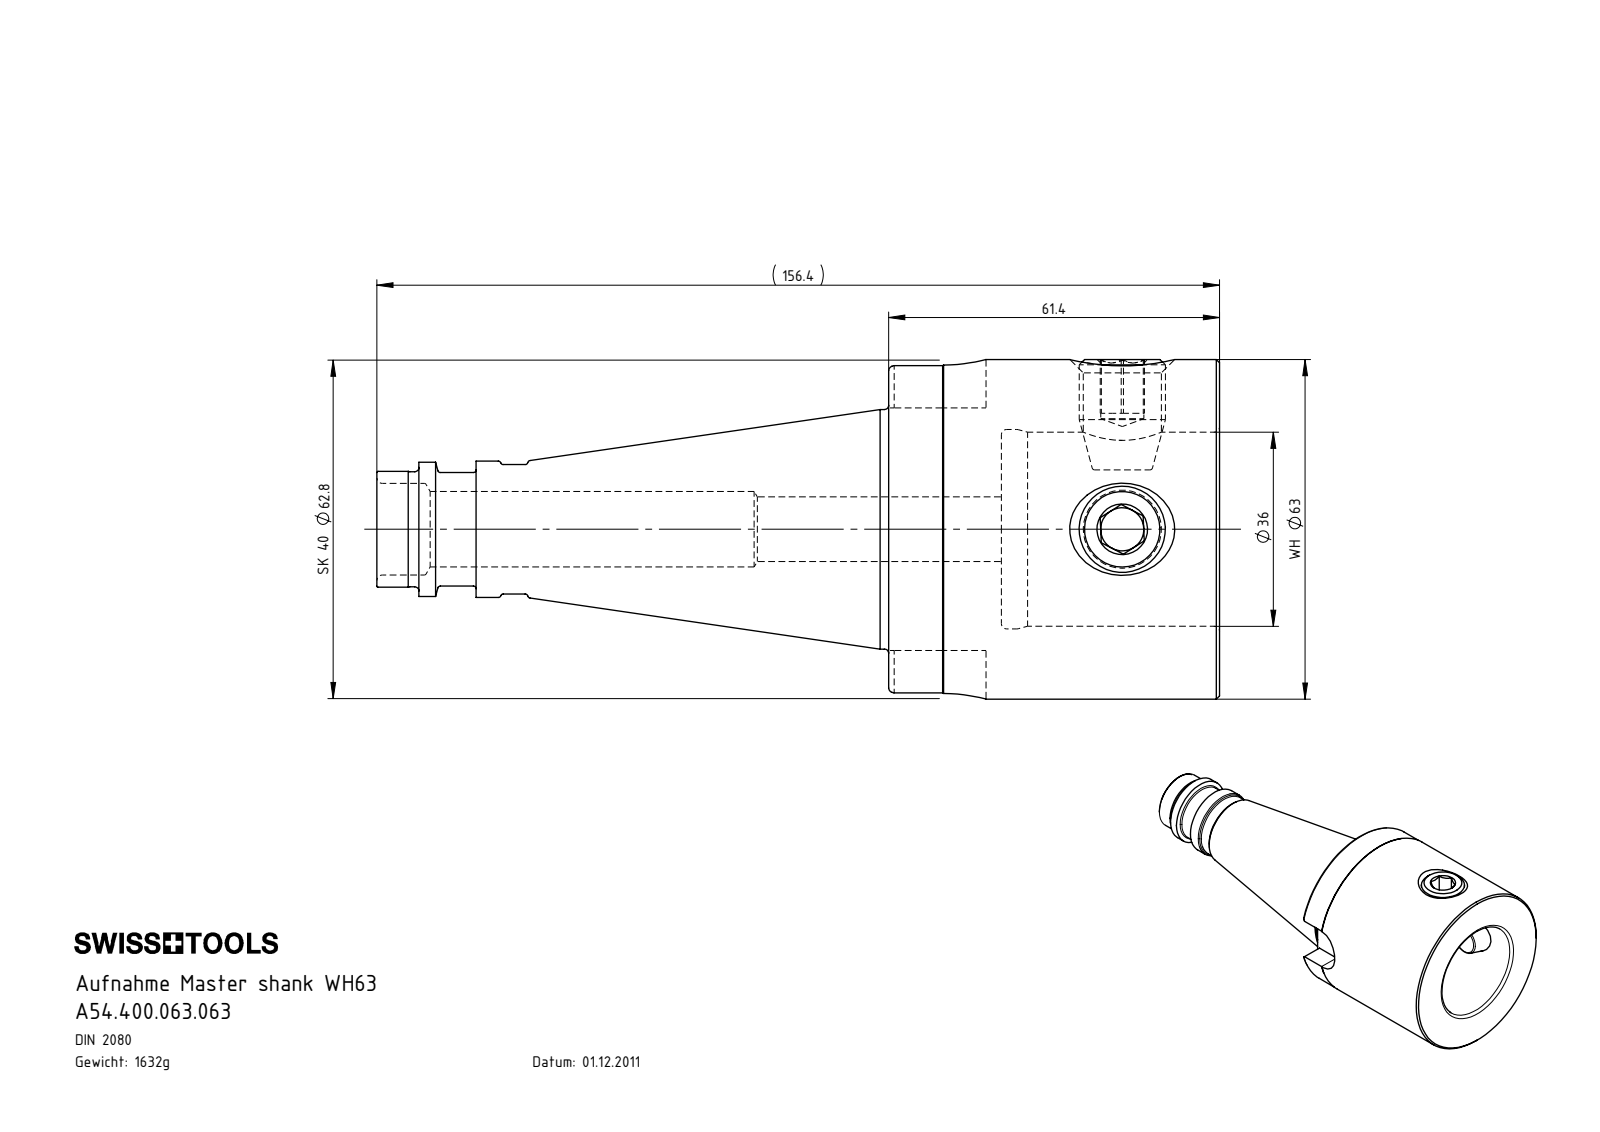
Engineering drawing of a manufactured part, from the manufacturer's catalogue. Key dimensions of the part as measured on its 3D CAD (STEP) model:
Part name (STEP PRODUCT): WH6-ER1.001.021; SZ4-WH6.K01.063_B; A54.400.063.063
STEP written by: SolidWorks 2015 (AUTOMOTIVE_DESIGN)
Units: millimetres
Bodies: 3 solids, 161 faces (47 planar, 43 cylindrical, 71 other)
Overall size (bounding box): 156.4 × 63 × 63
Volume: 207 874 mm³ · Surface area: 40 045 mm²
Round holes (diameter × count): ⌀8 ×2, ⌀14.5 ×2, ⌀12 ×1, ⌀14 ×1, ⌀17 ×1, ⌀36 ×1, ⌀37 ×1
Round bosses / shafts (diameter × count): ⌀16 ×2, ⌀63 ×1, ⌀62.8 ×1, ⌀44.45 ×1, ⌀25.3 ×1, ⌀24.91 ×1, ⌀24 ×1, ⌀21.5 ×1
Partial cylindrical surfaces — rounded edges, fillets, slot ends (radius × count): R8.05 ×1
Main face-to-face distances: 61.4, 20.9, 40.5, 45, 8, 20.5, 16.1, 76.6, 97.5, 138
